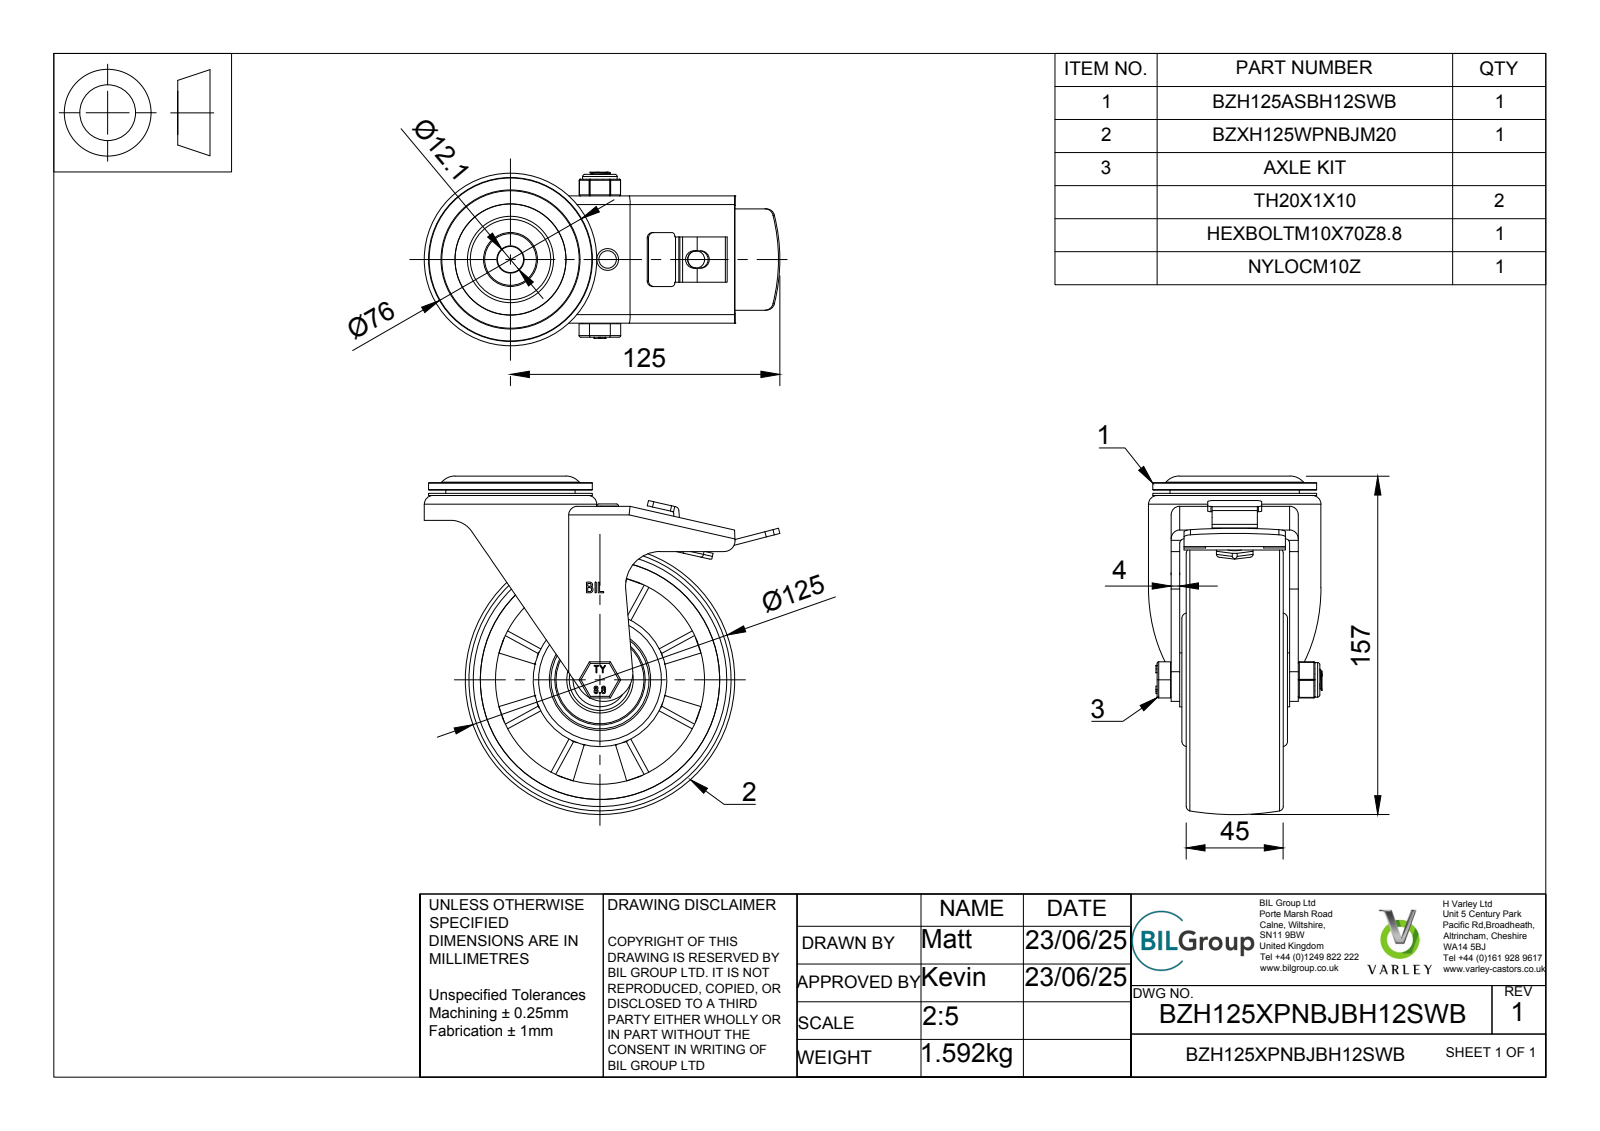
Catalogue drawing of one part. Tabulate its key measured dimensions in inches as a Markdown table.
| quantity | value |
| --- | --- |
| part name | BZH125XPNBJBH12SWB v3; BZH125ASBH12SWB v1; ZINC PLATED, PRESSED STEEL TOP HEAD; ZINC PLATED, PRESSED STEEL FORKS (+8 more) |
| STEP written by | Autodesk Translation Framework v14.10.0.0 (AUTOMOTIVE_DESIGN) |
| units | inches |
| bodies | 42 solids, 1403 faces (669 planar, 230 cylindrical, 504 other) |
| overall size | 6.496 × 6.181 × 3.169 |
| volume | 30.9 in³ |
| surface area | 352.1 in² |
| round holes (diameter × count) | 0.236 × 1, 0.315 × 1, 0.394 × 1, 0.402 × 1, 0.413 × 1, 0.472 × 1, 0.476 × 1, 0.787 × 1, 1.122 × 1, 1.181 × 1, 1.213 × 1, 1.26 × 1 |
| round bosses / shafts (diameter × count) | 0.984 × 2, 3.15 × 1, 2.992 × 1, 2.441 × 1, 2.362 × 1, 1.606 × 1, 1.535 × 1, 1.232 × 1 |
| partial cylindrical surfaces (radius × count) | 0.02 × 18, 0.079 × 13, 0.157 × 10, 0.059 × 8, 0.03 × 6, 0.039 × 2, 0.098 × 2, 0.197 × 1 |
| main face-to-face distances | 0.197, 0.276, 0.157, 0.472, 0.039, 1.378, 0.079, 0.098, 0.118, 0.059 |
| hole center spacings | 1.774 |
